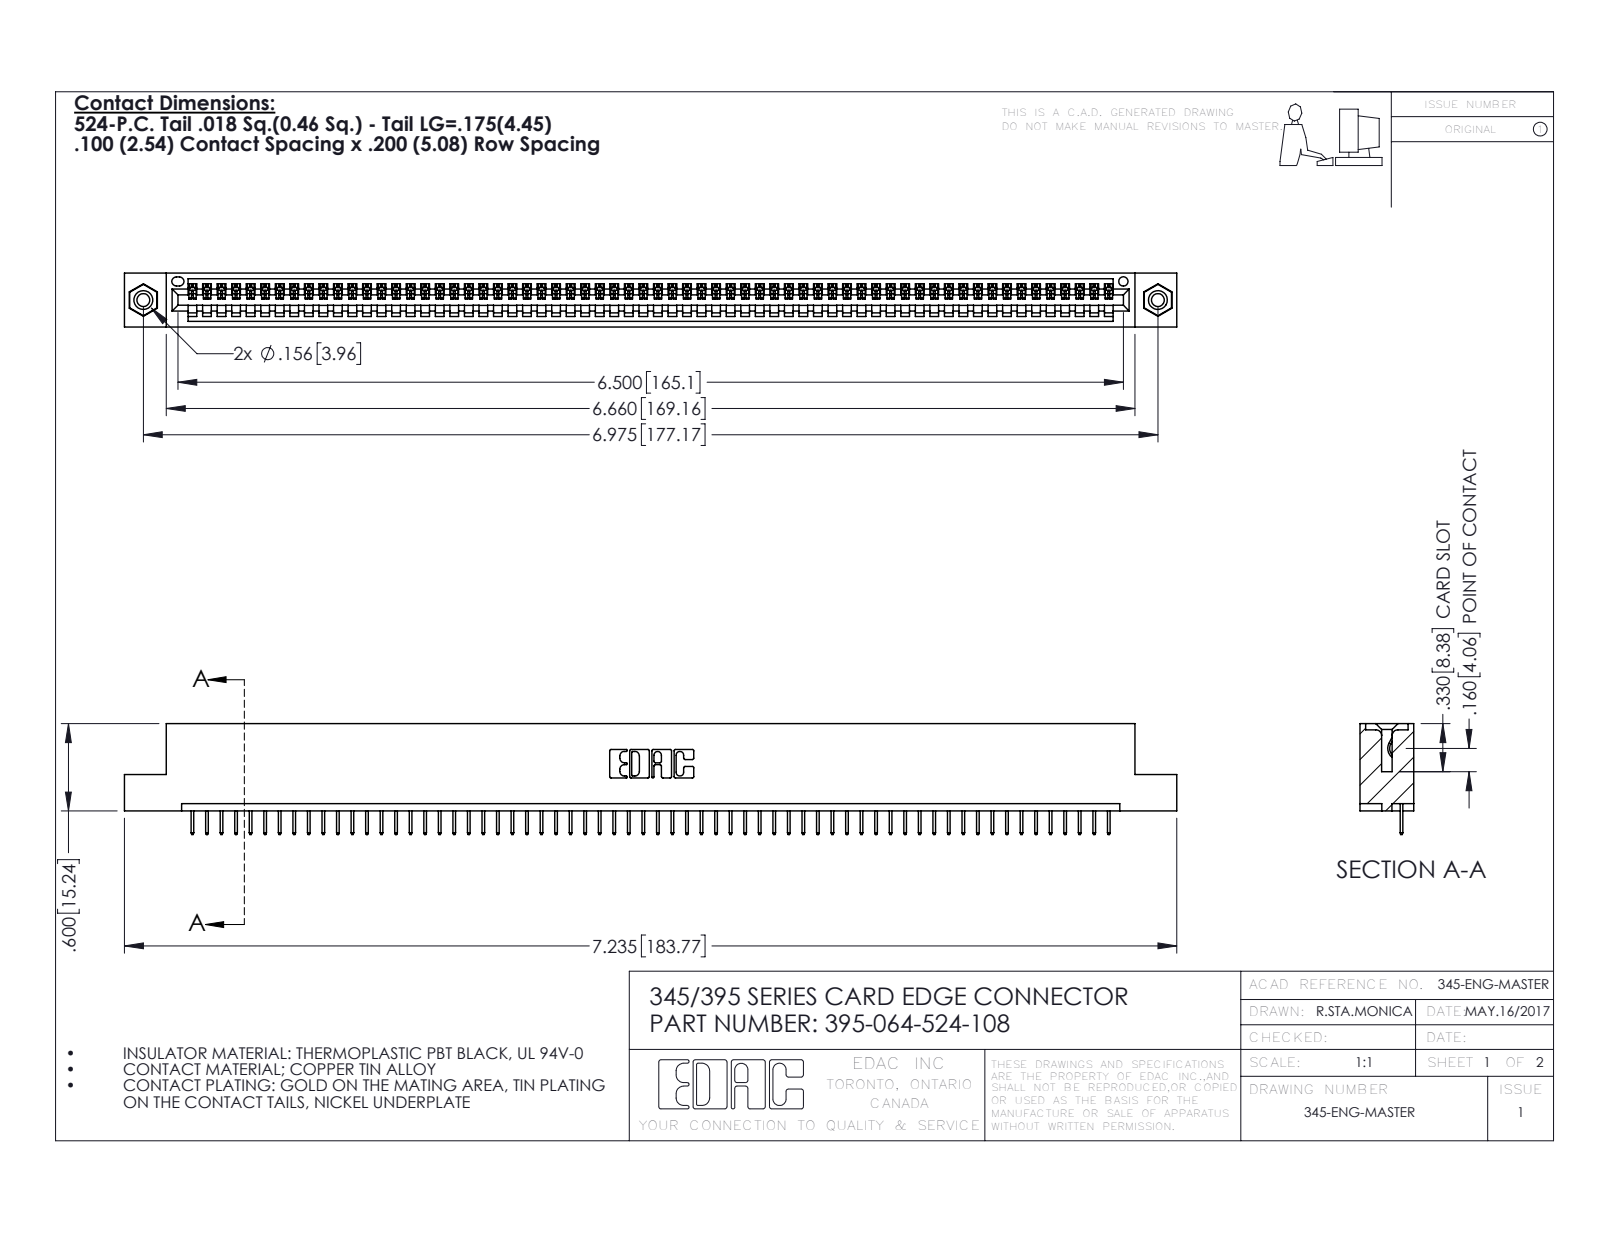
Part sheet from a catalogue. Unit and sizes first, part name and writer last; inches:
Units: inches
Overall size (bounding box): 7.235 × 0.762 × 0.37
Round holes (diameter × count): ⌀0.089 ×2, ⌀0.125 ×2, ⌀0.156 ×2, ⌀0.064 ×1
Round bosses / shafts (diameter × count): ⌀0.155 ×2
Partial cylindrical surfaces — rounded edges, fillets, slot ends (radius × count): R0.006 ×128, R0.01 ×22, R0.007 ×6, R0.031 ×6, R0.026 ×3, R0.031 ×2, R0.04 ×2, R0.014 ×1
Main face-to-face distances: 0.072, 0.298, 0.37, 0.2, 0.098, 0.272, 0.025, 0.225, 0.072, 0.149
Hole centre spacings: 0.27, 6.739, 6.975
Volume: 1.06 in³ · Surface area: 35.03 in²
Bodies: 67 solids, 4154 faces (3056 planar, 1082 cylindrical, 16 other)
Part name (STEP PRODUCT): 345 Part_Flush Mounting Lugs - 0.156 Dia-TI; 345-292-001_345-293-124; 345-250-001_345-250-003-102; 395-064-524-108
STEP written by: SolidWorks 2016 (CONFIG_CONTROL_DESIGN)
